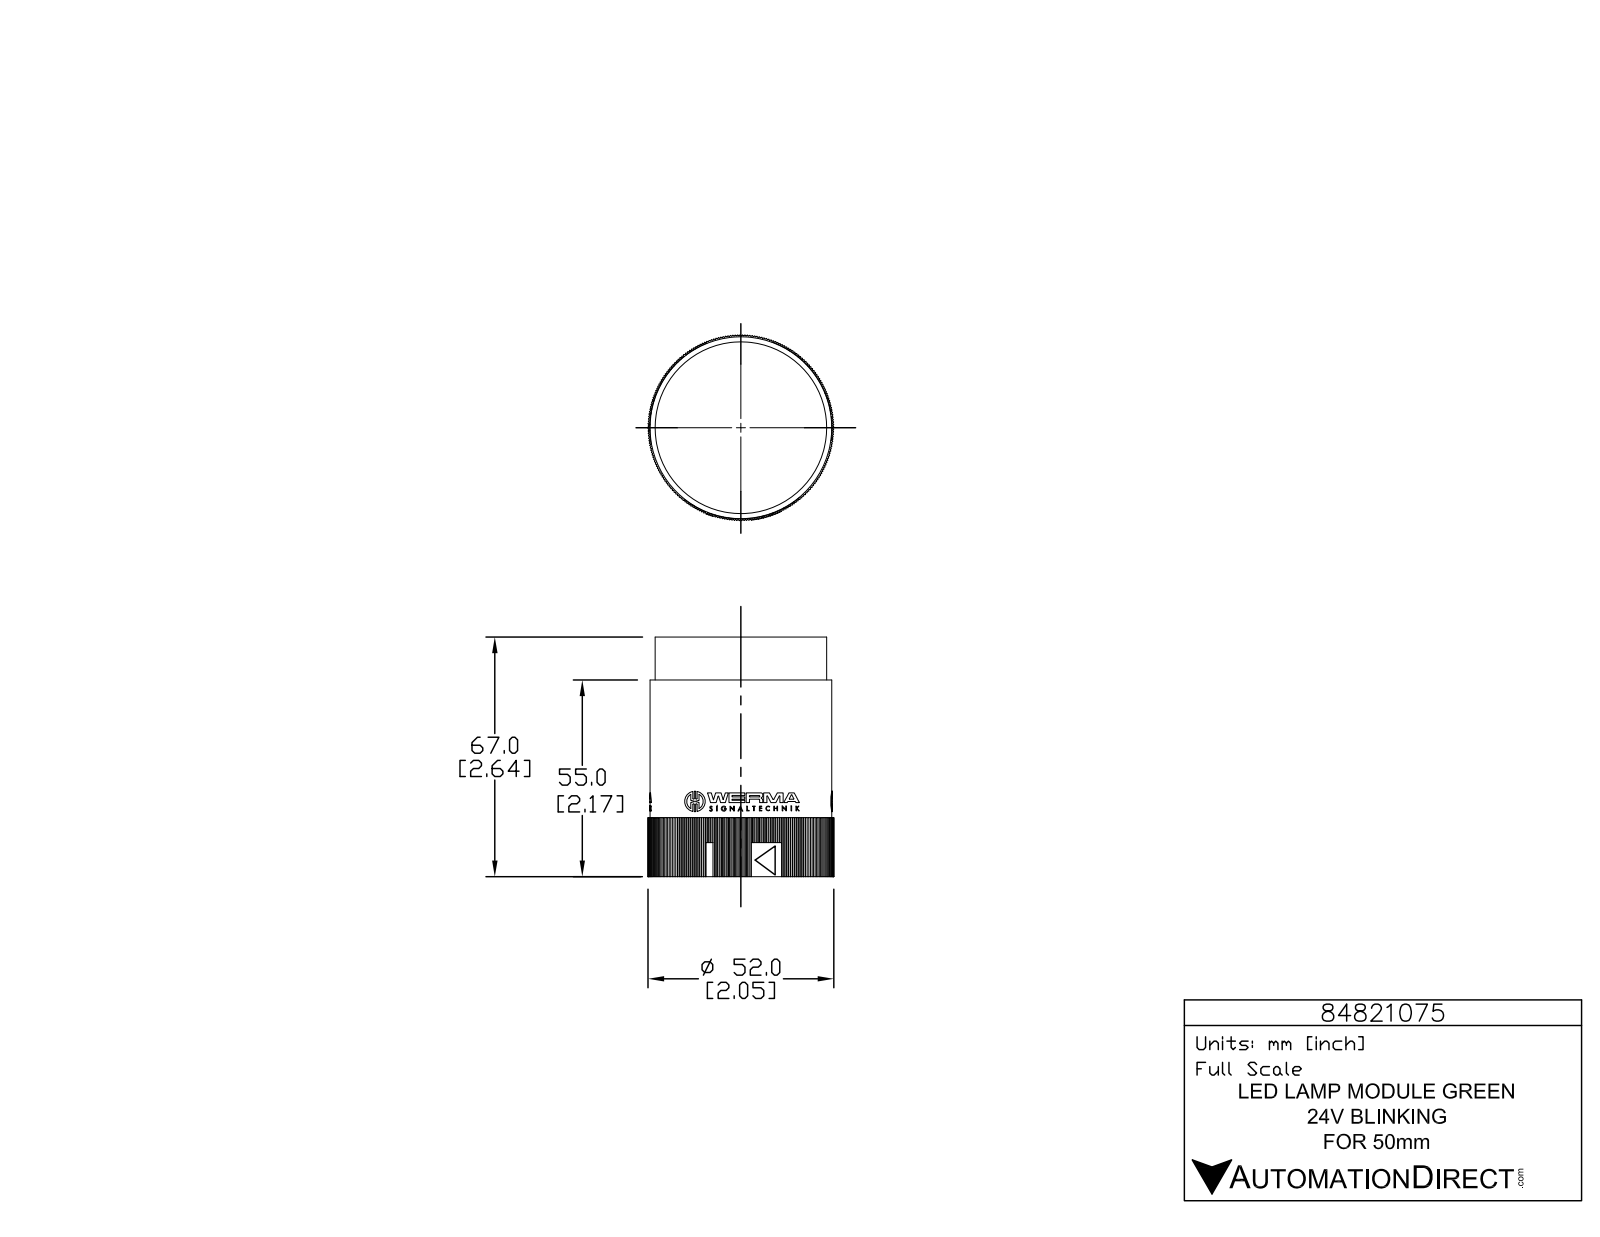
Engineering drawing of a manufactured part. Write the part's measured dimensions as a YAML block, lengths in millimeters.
part_name: "84821075"
step_written_by: "SolidWorks 2015 (AUTOMOTIVE_DESIGN)"
units: millimeters
bodies: {solids: 1, faces: 1265, planar: 1020, cylindrical: 245, other: 0}
overall_size: [67, 52, 52]
volume: 112600
surface_area: 17820
round_holes:
  - {diameter: 1, count: 3}
  - {diameter: 48.2, count: 1}
round_bosses_or_shafts:
  - {diameter: 5.7, count: 3}
  - {diameter: 1.4, count: 3}
  - {diameter: 50.9, count: 1}
  - {diameter: 48, count: 1}
partial_cylinders:
  - {radius: 0.2, count: 6}
  - {radius: 0.2, count: 6}
  - {radius: 0.2, count: 6}
  - {radius: 3.3, count: 6}
  - {radius: 0.1, count: 3}
  - {radius: 0.1, count: 3}
  - {radius: 0.2, count: 3}
  - {radius: 0.2, count: 3}
face_to_face_distances: [55, 36.3, 36.3, 36.3, 12, 67, 36.3, 36.3, 43, 50.5]
